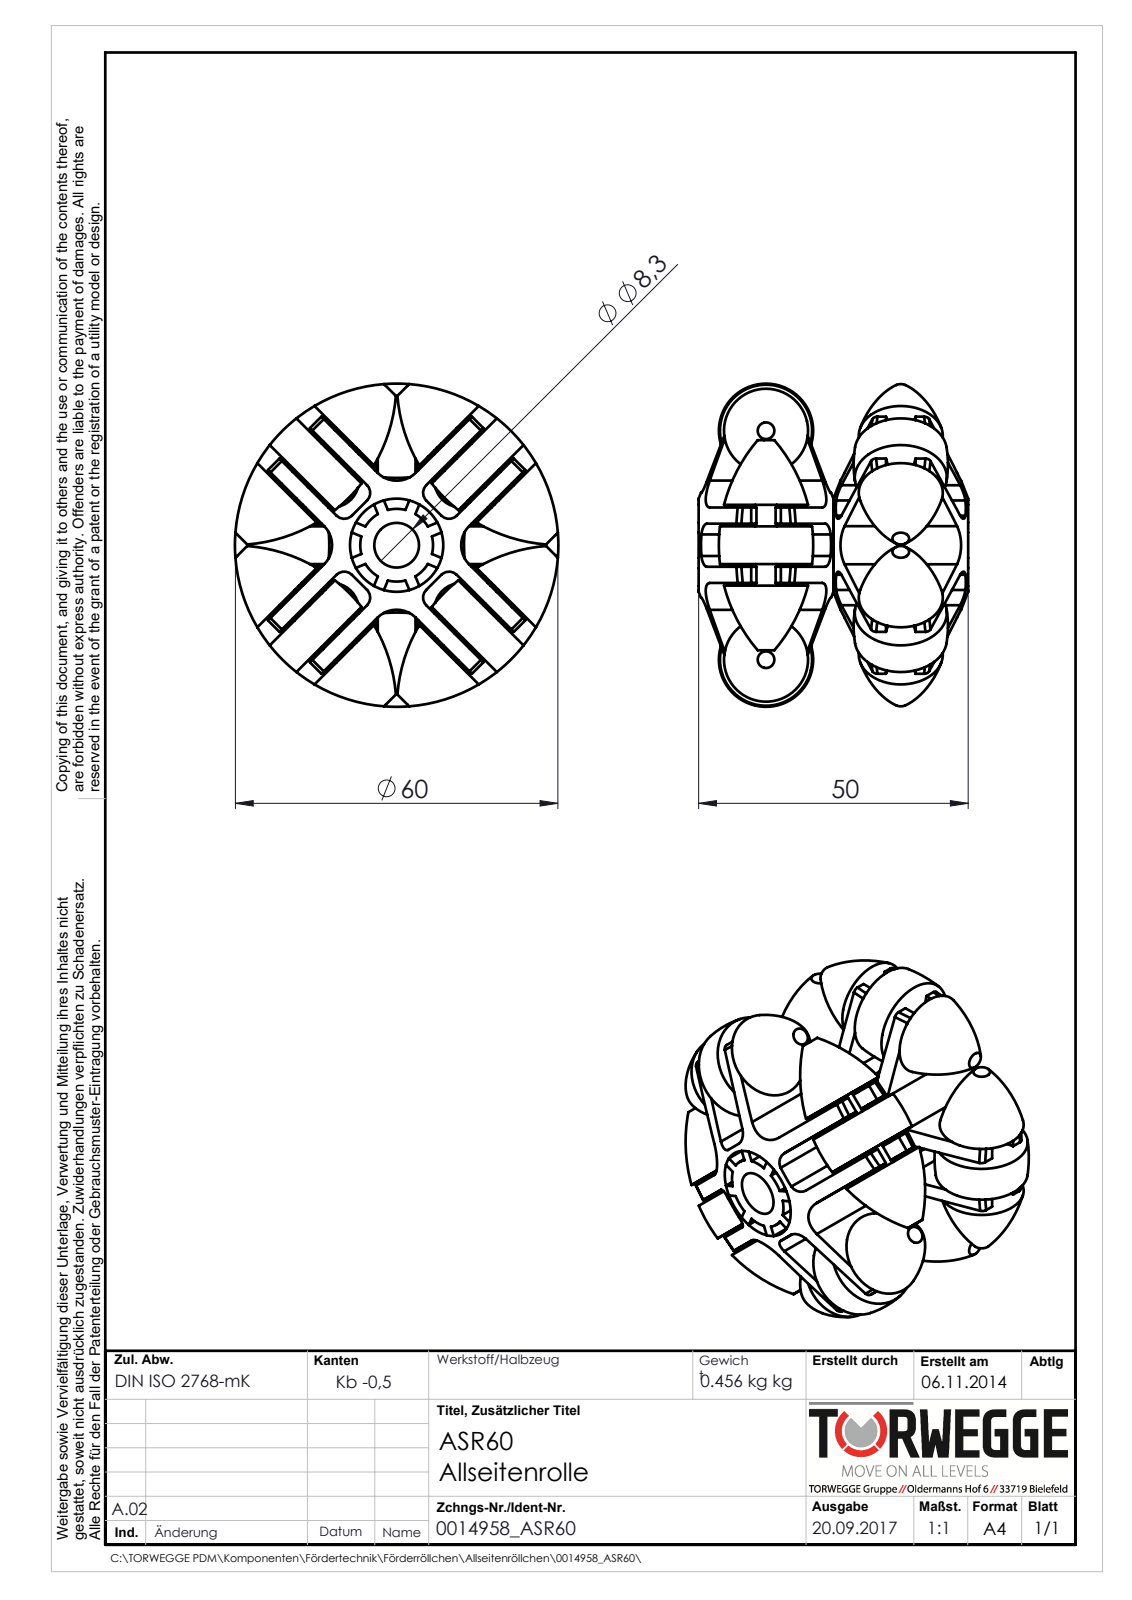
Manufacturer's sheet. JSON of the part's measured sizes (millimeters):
{"part_name": "ASR60_Roellchen; ASR60_Achse; ASR60_Halter_Steg; 0014958_ASR60 (+1 more)", "step_written_by": "SolidWorks 2016 (AUTOMOTIVE_DESIGN)", "units": "millimeters", "bodies": {"solids": 34, "faces": 635, "planar": 332, "cylindrical": 183, "other": 120}, "overall_size": [60, 60, 50], "volume_mm3": 57733, "surface_area_mm2": 43080, "round_holes": [[4, 8], [8.3, 1], [10.5, 1], [17.3, 1]], "round_bosses_or_shafts": [[13.5, 1]], "partial_cylinders_radius": [[2, 20], [5, 8]], "face_to_face_distances": [0.5, 3.5, 11, 3, 7.5, 10.5, 14.5, 4, 11.5, 8], "hole_center_spacings": [42.5]}
